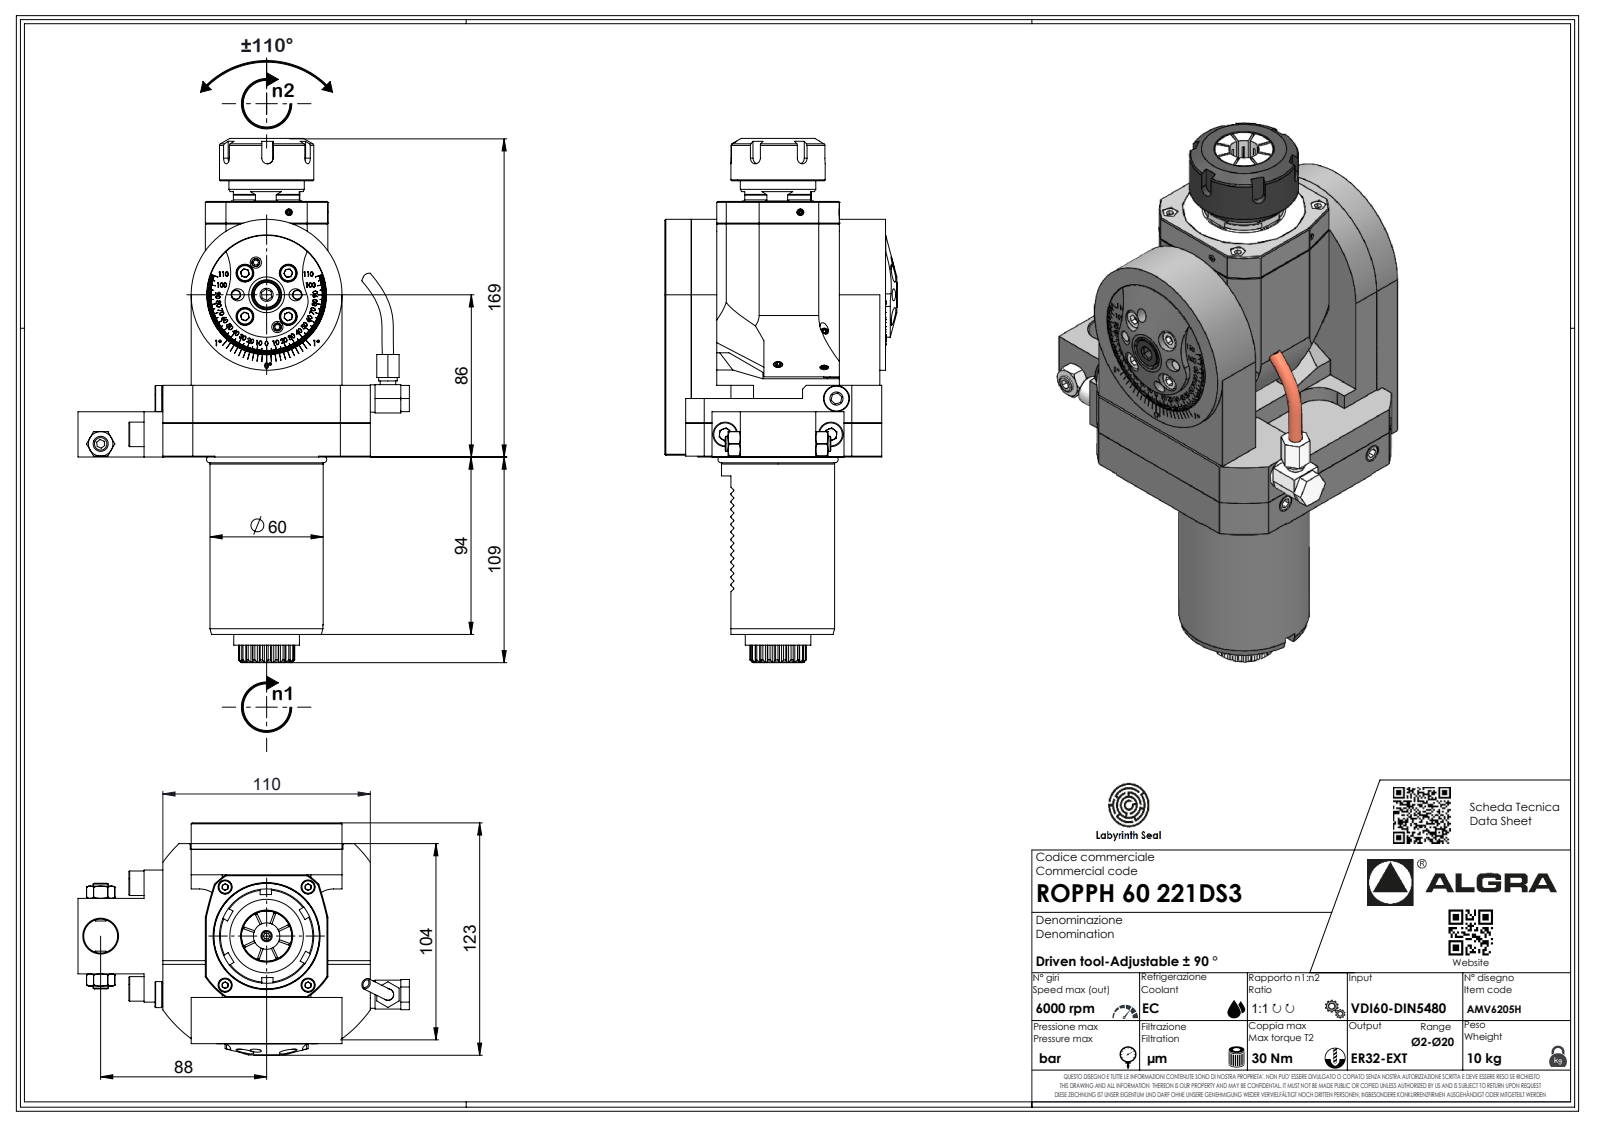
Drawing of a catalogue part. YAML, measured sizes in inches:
part_name: "ROPPH60221DS3"
step_written_by: "SolidWorks 2023 (AUTOMOTIVE_DESIGN)"
units: inches
bodies: {solids: 1, faces: 919, planar: 597, cylindrical: 166, other: 156}
overall_size: [10.941, 6.917, 4.843]
volume: 75.36
surface_area: 192.3
round_holes:
  - {diameter: 0.083, count: 1}
  - {diameter: 1.969, count: 1}
round_bosses_or_shafts:
  - {diameter: 3.15, count: 1}
  - {diameter: 2.362, count: 1}
  - {diameter: 2.311, count: 1}
  - {diameter: 1.575, count: 1}
  - {diameter: 1.37, count: 1}
  - {diameter: 0.571, count: 1}
  - {diameter: 0.386, count: 1}
  - {diameter: 0.323, count: 1}
partial_cylinders:
  - {radius: 0.012, count: 14}
  - {radius: 0.013, count: 7}
  - {radius: 0.02, count: 7}
  - {radius: 0.146, count: 7}
  - {radius: 0.118, count: 5}
  - {radius: 0.008, count: 3}
  - {radius: 0.394, count: 2}
  - {radius: 0.472, count: 2}
face_to_face_distances: [0.886, 3.445, 2.559, 3.15, 0.295, 3.74, 0.591, 0.276, 5.335, 1.083]
